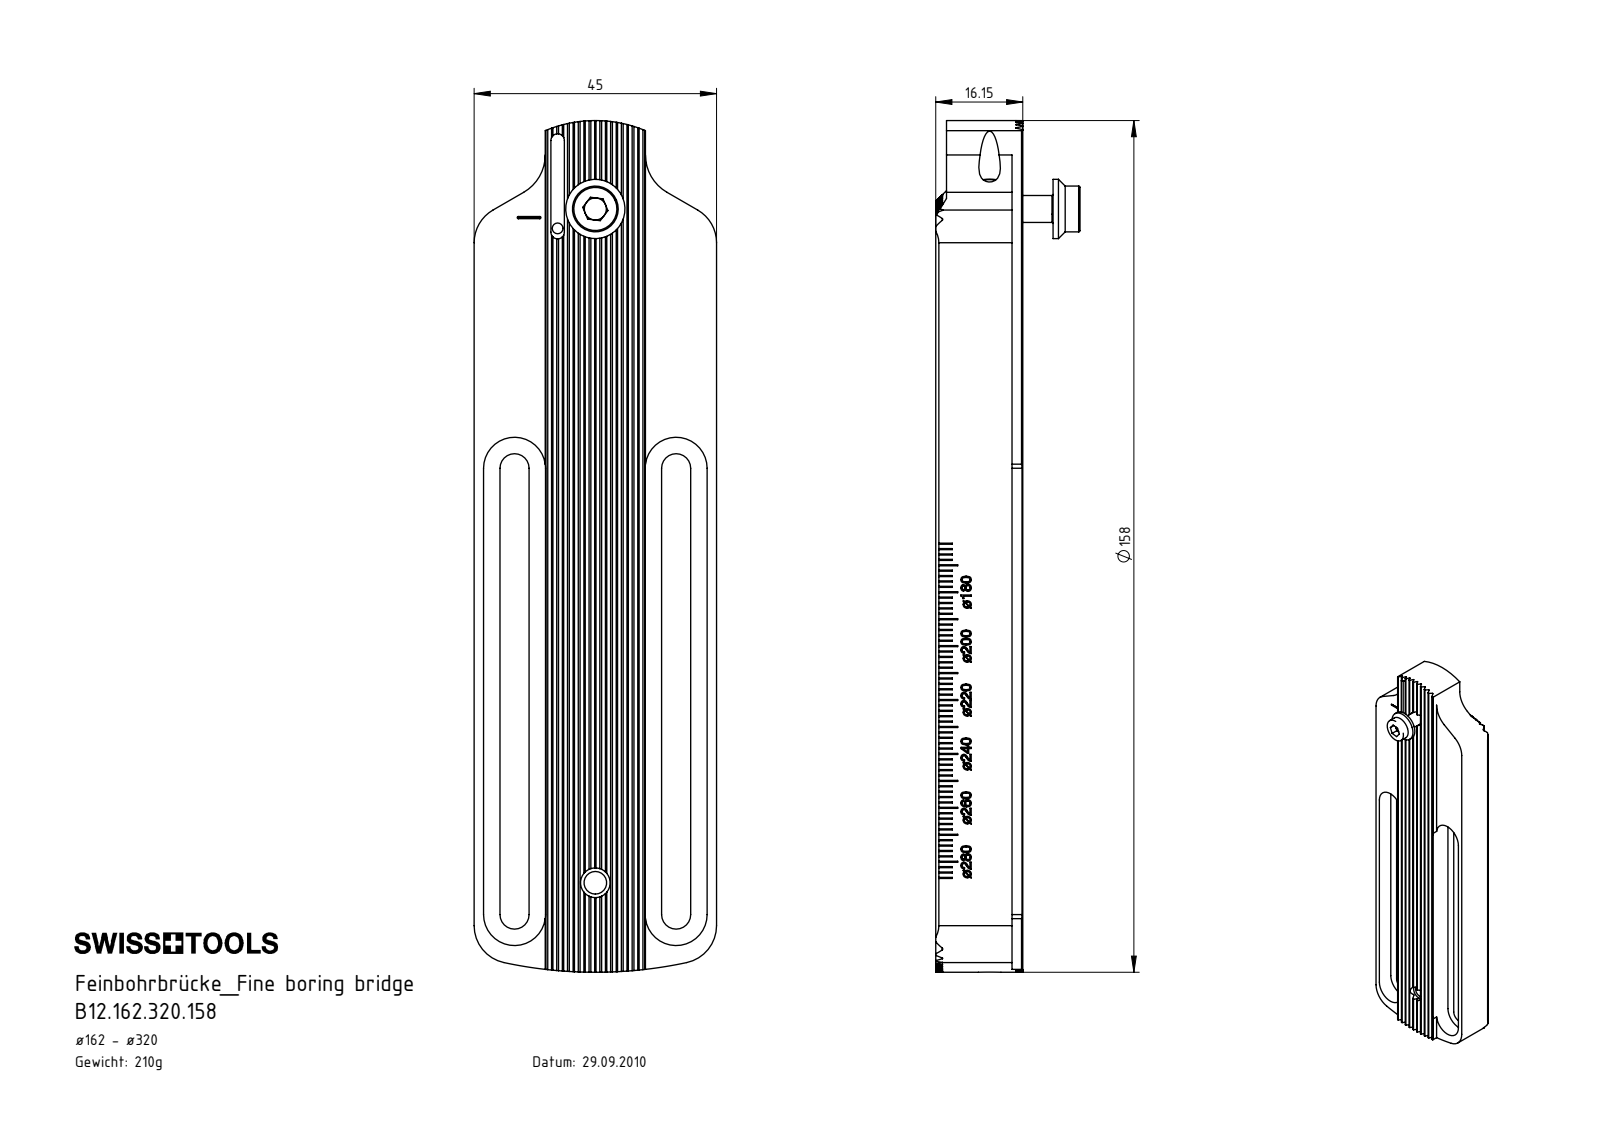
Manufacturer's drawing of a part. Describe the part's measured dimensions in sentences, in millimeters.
The part is named "BN 1392 - M5 x 16; BV2-WCA.K11.014_B; MH1-BV2.K02.015_B; B12.162.320.158 (+5 more)". Its 3-D file was written by "SolidWorks 2017 (CONFIG_CONTROL_DESIGN)". It is 13 solids with 1594 faces: 916 planar, 225 cylindrical and 453 other. Overall it measures 160.5 by 45 by 29.58 millimeters. Its volume is 79 040 cubic millimeters and its surface area 35 974 square millimeters. Round holes: 6 of diameter 4.2, 5 of diameter 2, 5 of diameter 3.3, 2 of diameter 5.5, 1 of diameter 2.05, 1 of diameter 2.38, 1 of diameter 2.8, 1 of diameter 3, 1 of diameter 3.85. Round bosses or shafts: 5 of diameter 4, 1 of diameter 11, 1 of diameter 8.5, 1 of diameter 5, 1 of diameter 3.4, 1 of diameter 3, 1 of diameter 2.5. Partial cylindrical surfaces (rounded edges, fillets, slot ends): 41 of radius 0.14, 6 of radius 0.21, 6 of radius 2.7, 6 of radius 5.75, 5 of radius 0.36, 4 of radius 7, 2 of radius 1.25, 2 of radius 8. The main face-to-face distances are 1.73, 8.66, 3.46, 6.93, 5.2, 5.77, 10.39, 16.16, 3.05, 8.45. The hole center spacings are 20, 1, 3.89, 4.01, 7.87, 8.38, 11.07, 21.4.
